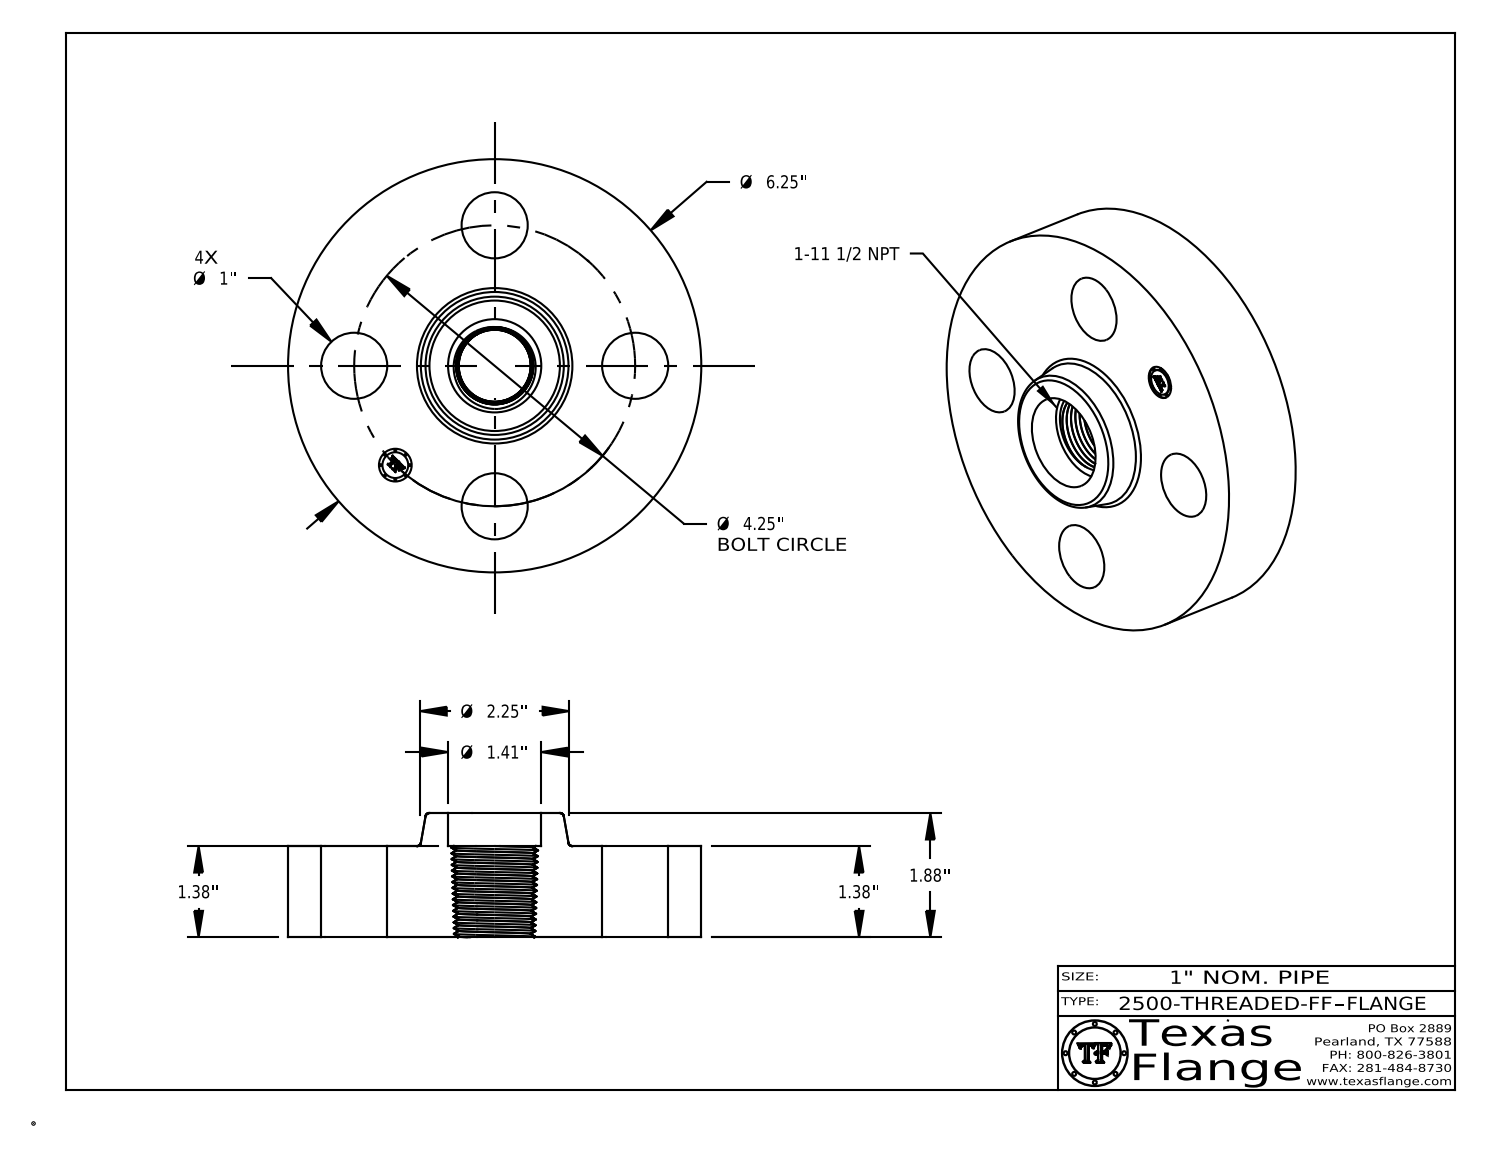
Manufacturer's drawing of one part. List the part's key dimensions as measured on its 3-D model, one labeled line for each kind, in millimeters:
Part name (STEP PRODUCT): 2500-THREADED-FF
STEP written by: CATIA V5 STEP AP214 (AUTOMOTIVE_DESIGN)
Units: millimetres
Bodies: 1 solid, 570 faces (369 planar, 32 cylindrical, 169 other)
Overall size (bounding box): 158.8 × 158.8 × 47.8
Volume: 614 500 mm³ · Surface area: 72 190 mm²
Round holes (diameter × count): ⌀25.4 ×4, ⌀12.6 ×1, ⌀35.8 ×1
Round bosses / shafts (diameter × count): ⌀0.8 ×8, ⌀158.8 ×1, ⌀9.9 ×1
Main face-to-face distances: 35.1, 47.8, 12.7, 34.7, 0.4, 13.1, 3.8, 3.7, 0.7, 2.4
Hole centre spacings: 54, 76.4, 41.3, 99.7, 108
